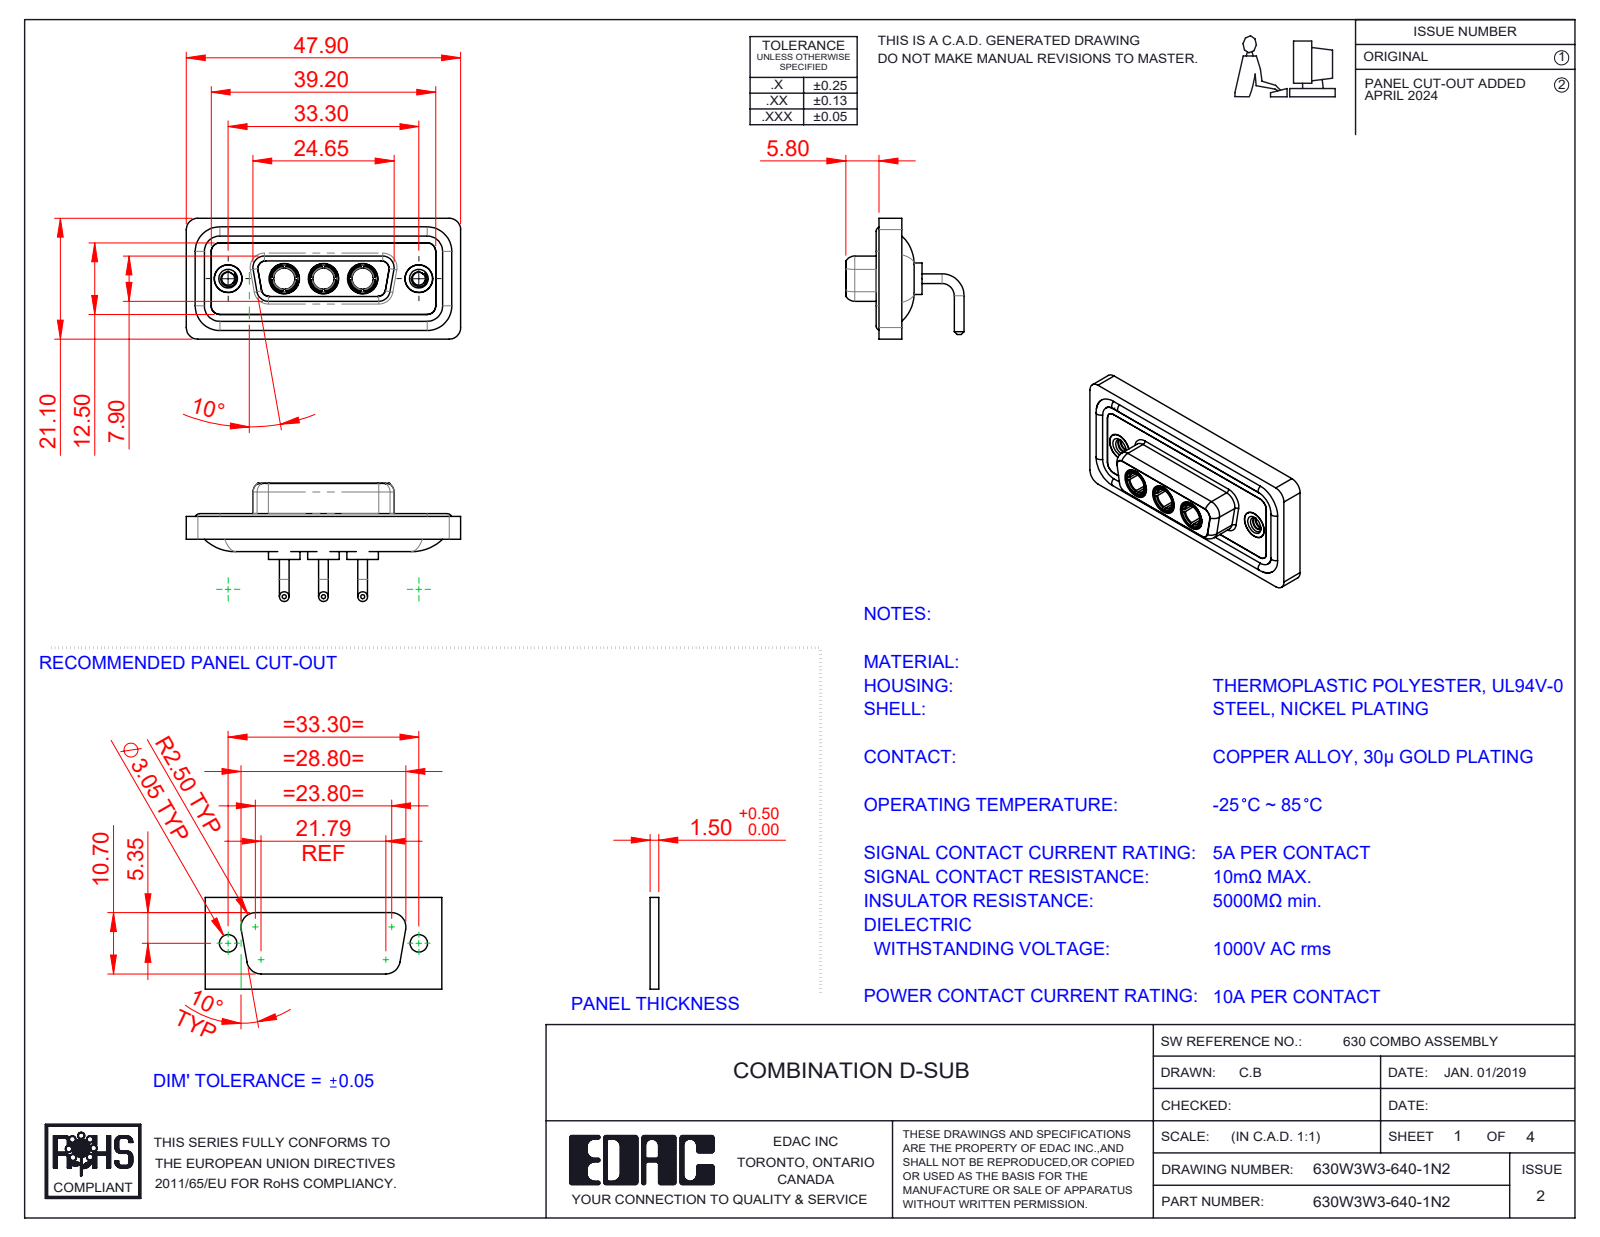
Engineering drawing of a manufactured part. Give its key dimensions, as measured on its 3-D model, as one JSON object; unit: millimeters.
{"part_name": "630Combo Threaded Rivet_2; 630Combo Shell Rear_15 Contacts; 630Combo Shell Front_15 Contacts; Power Socket_10A RA (+3 more)", "step_written_by": "SolidWorks 2023 (CONFIG_CONTROL_DESIGN)", "units": "millimeters", "bodies": {"solids": 13, "faces": 620, "planar": 192, "cylindrical": 263, "other": 165}, "overall_size": [47.9, 21.1, 20.65], "volume_mm3": 6006, "surface_area_mm2": 9819, "round_holes": [[4.85, 5], [3.7, 3], [5.3, 3], [2.26, 2], [4, 2], [4.05, 2], [5, 2]], "round_bosses_or_shafts": [[1.7, 6], [1.6, 4], [5.5, 3], [5.2, 3], [4.96, 3], [4.75, 3], [3.75, 3], [4.95, 2]], "partial_cylinders_radius": [[2, 20], [1.5, 18], [1.35, 12], [1.6, 8], [0.25, 4], [0.5, 4], [0.6, 4], [0.65, 4]], "face_to_face_distances": [0.4, 1.8, 1.1, 1.6, 2.9, 2.5, 3.1, 3.7, 1.5, 4.1], "hole_center_spacings": [6.85, 9.8, 16.65, 23.5, 13.7, 33.3]}
